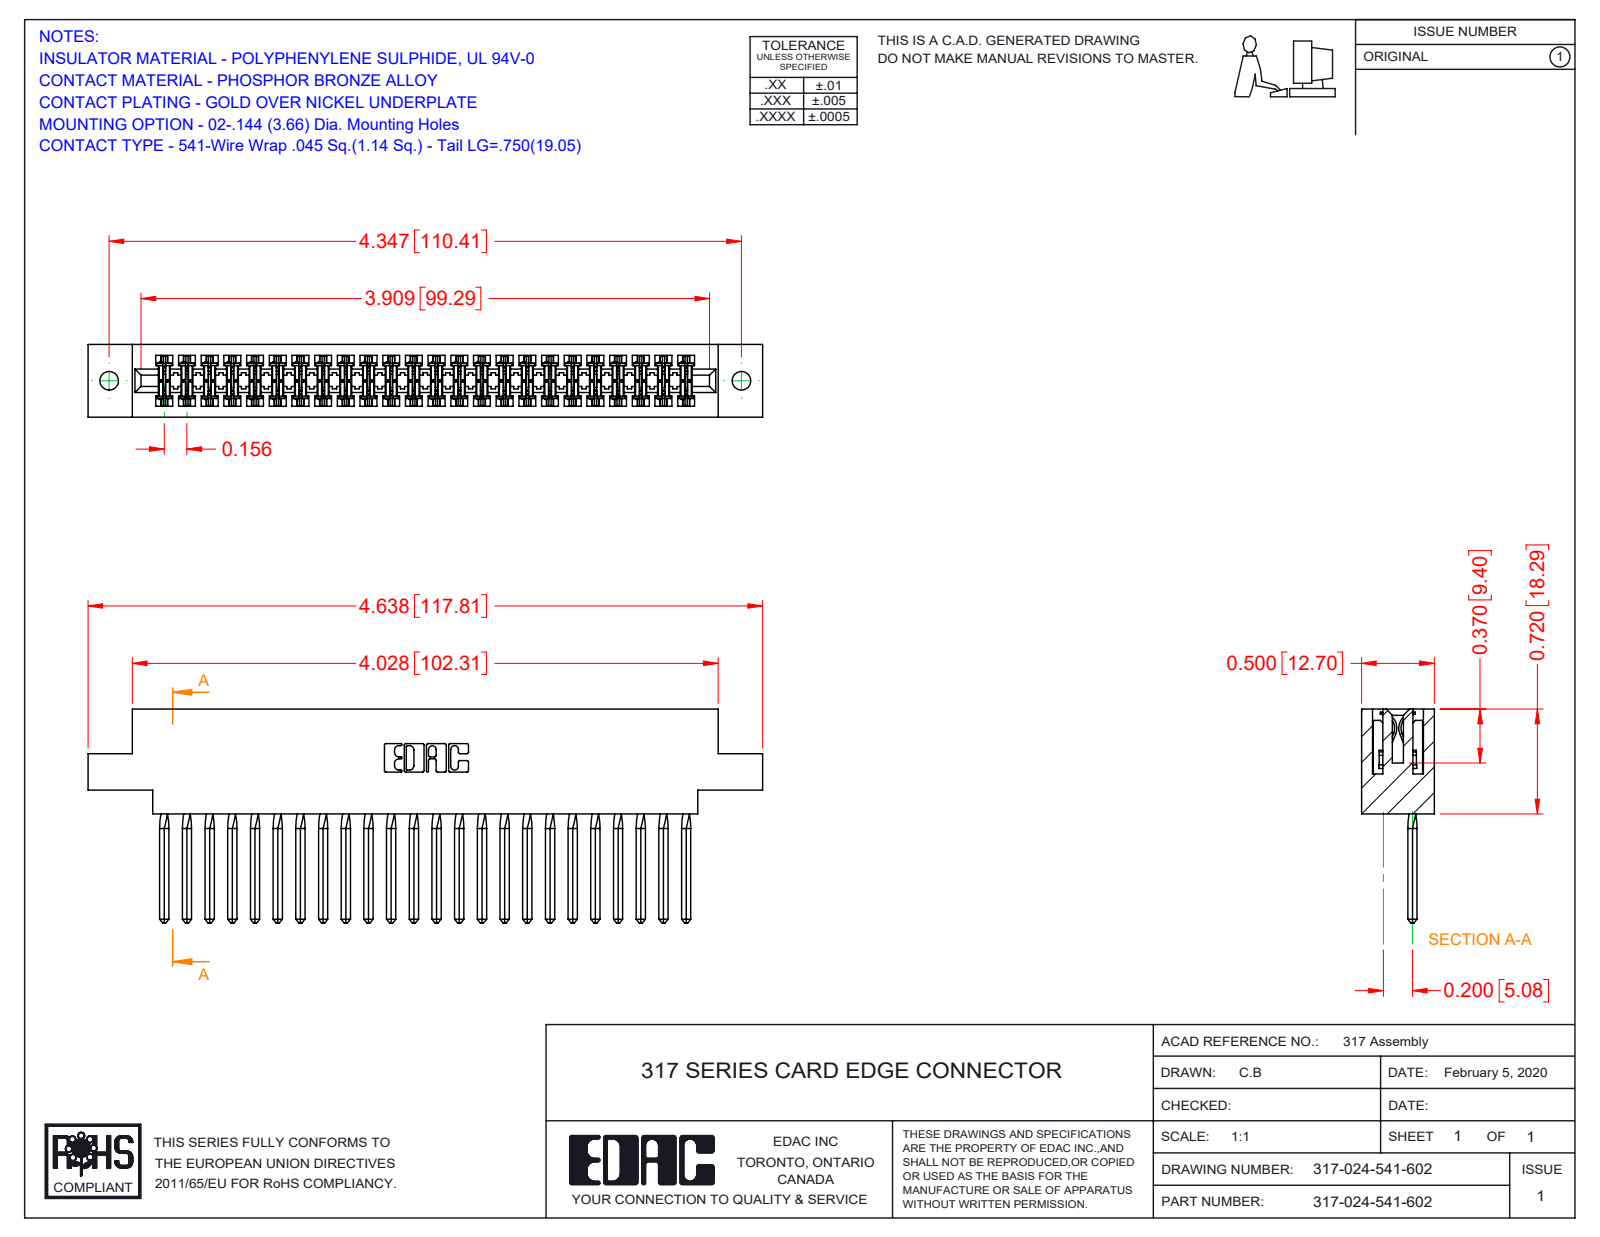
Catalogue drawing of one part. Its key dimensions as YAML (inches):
part_name: "317-290-002_541; 317 Part_.144 Dia; 317-024-541-602"
step_written_by: "SolidWorks 2016 (CONFIG_CONTROL_DESIGN)"
units: inches
bodies: {solids: 25, faces: 3750, planar: 3034, cylindrical: 620, other: 96}
overall_size: [4.638, 1.47, 0.5]
volume: 1.13
surface_area: 39.21
round_holes:
  - {diameter: 0.128, count: 2}
partial_cylinders:
  - {radius: 0.015, count: 48}
  - {radius: 0.01, count: 22}
  - {radius: 0.007, count: 6}
  - {radius: 0.031, count: 6}
  - {radius: 0.026, count: 3}
  - {radius: 0.095, count: 2}
  - {radius: 0.1, count: 2}
  - {radius: 0.11, count: 2}
face_to_face_distances: [0.5, 0.075, 0.425, 0.11, 0.35, 0.195, 0.772, 0.72, 0.22, 0.211]
hole_center_spacings: [4.347]
